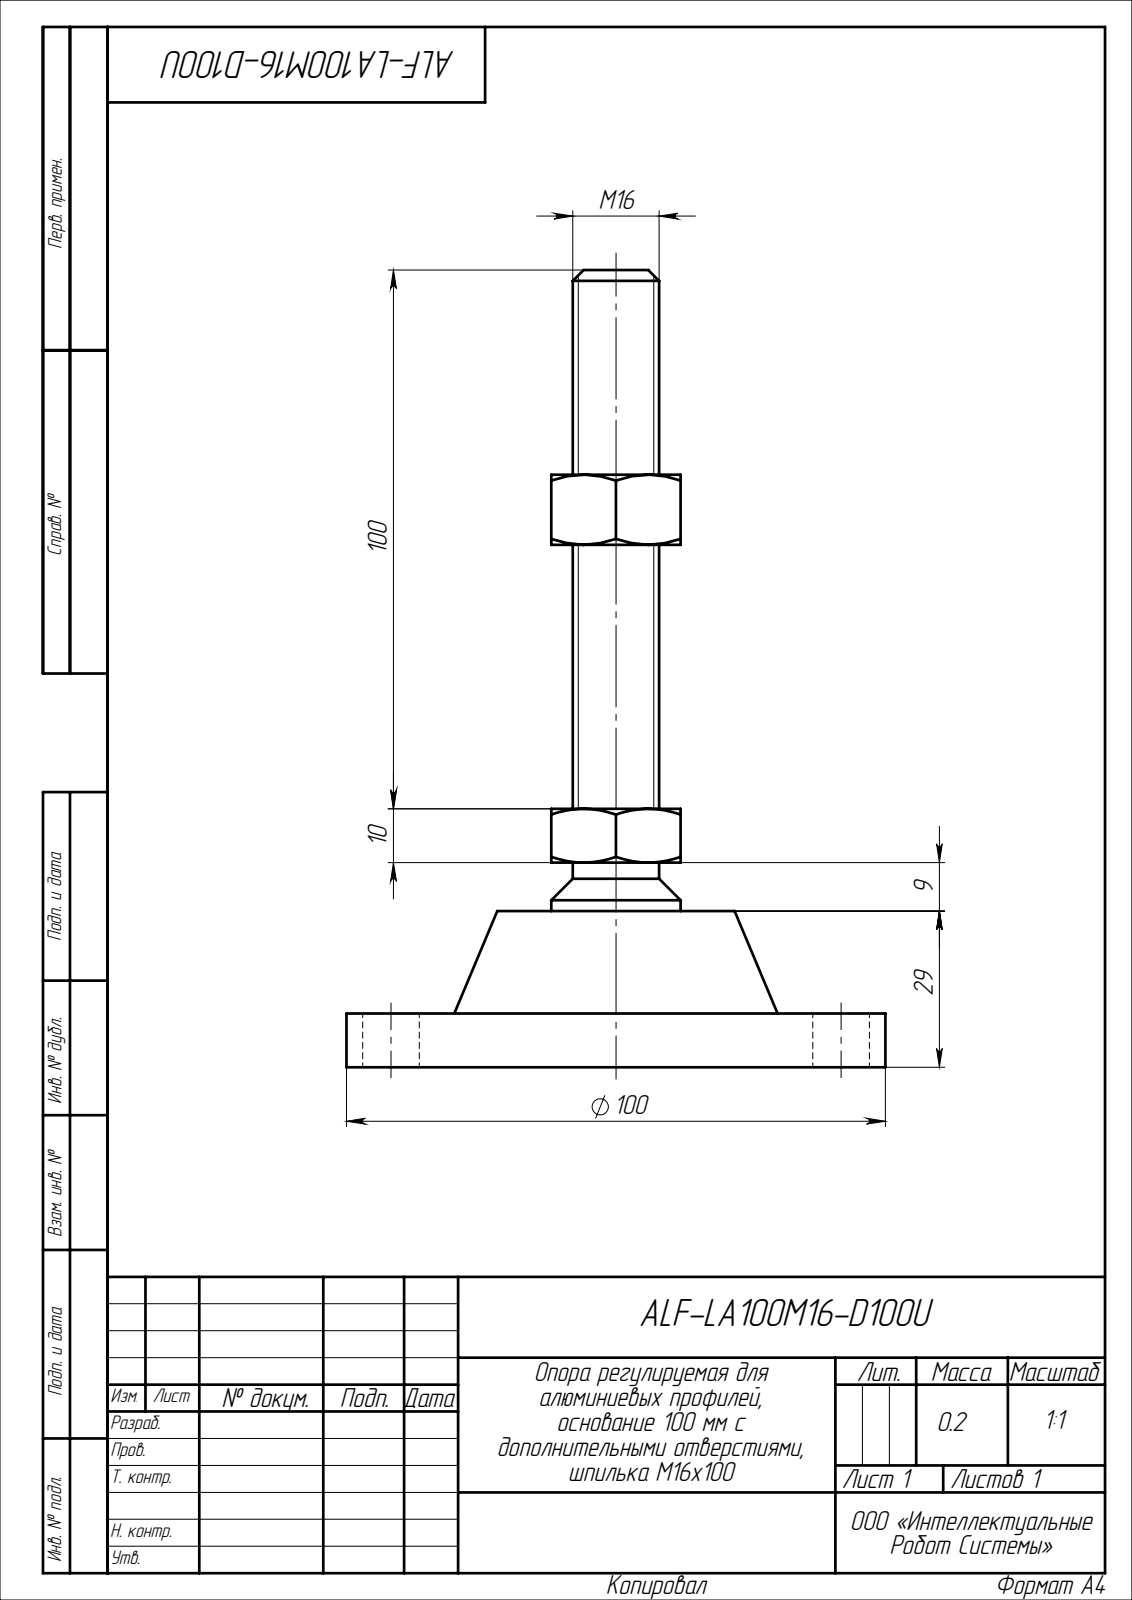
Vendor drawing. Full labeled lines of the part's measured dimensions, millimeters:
Part name (STEP PRODUCT): ALF-LA100M16-D100U
STEP written by: SolidWorks 2022 (CONFIG_CONTROL_DESIGN)
Units: millimetres
Bodies: 1 solid, 64 faces (20 planar, 14 cylindrical, 30 other)
Overall size (bounding box): 148 × 100 × 100
Volume: 149 072 mm³ · Surface area: 28 948 mm²
Round holes (diameter × count): ⌀10.5 ×2
Round bosses / shafts (diameter × count): ⌀100 ×1, ⌀24 ×1, ⌀16 ×1
Main face-to-face distances: 10, 19, 29, 24, 38, 110, 100, 81, 48, 62
Hole centre spacings: 83.5
